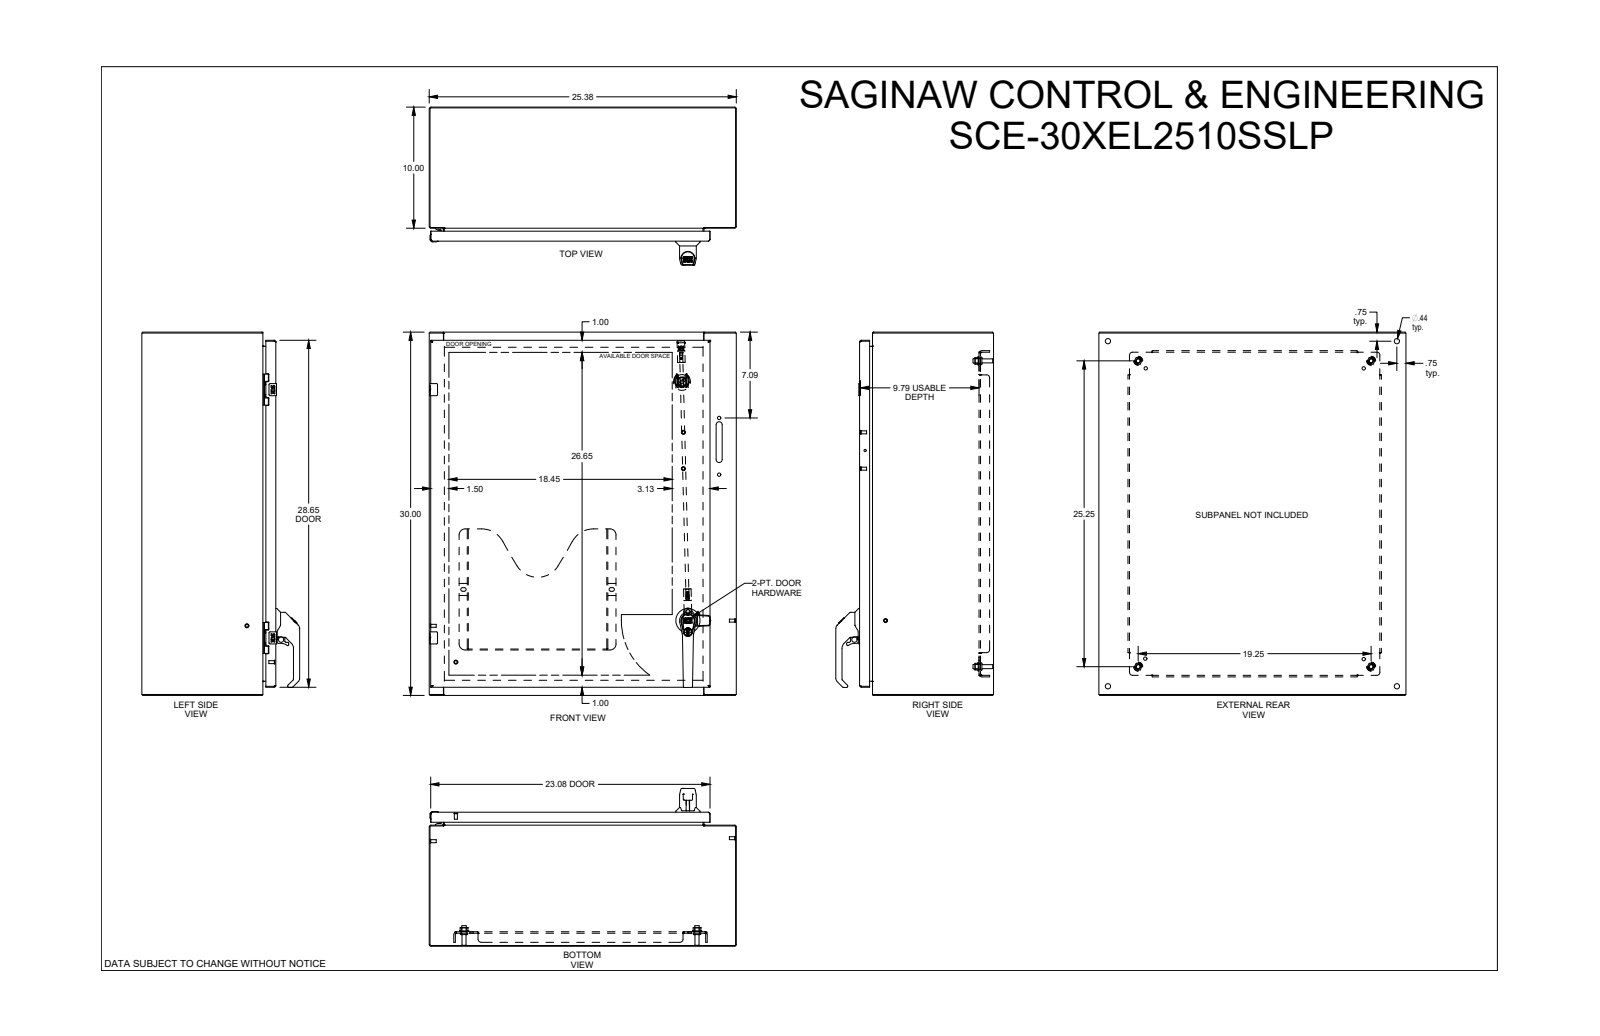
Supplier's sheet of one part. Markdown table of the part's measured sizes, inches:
| quantity | value |
| --- | --- |
| part name | SCE-30XEL2510SSLP |
| STEP written by | SolidWorks 2019 (CONFIG_CONTROL_DESIGN) |
| units | inches |
| bodies | 67 solids, 4628 faces (1743 planar, 1218 cylindrical, 1667 other) |
| overall size | 30 × 25.375 × 13.036 |
| volume | 329.1 in³ |
| surface area | 7 580 in² |
| round holes (diameter × count) | 0.281 × 6, 0.266 × 5, 0.172 × 4, 0.205 × 4, 0.244 × 4, 0.367 × 4, 0.437 × 4, 0.5 × 4, 0.25 × 3, 0.25 × 3, 0.375 × 3, 0.138 × 2 |
| round bosses / shafts (diameter × count) | 0.248 × 8, 0.17 × 6, 0.366 × 4, 0.332 × 4, 0.25 × 4, 0.563 × 3, 0.196 × 3, 0.341 × 2 |
| partial cylindrical surfaces (radius × count) | 0.03 × 69, 0.015 × 58, 0.01 × 36, 0.02 × 36, 0.02 × 34, 0.04 × 31, 0.039 × 30, 0.005 × 26 |
| main face-to-face distances | 0.075, 10.993, 10.918, 11.068, 1.125, 1.2, 9.868, 9.793, 0.075, 25.3 |
| hole center spacings | 20.5, 0.985, 0.02, 4.493, 0.472, 0.725, 0.854, 0.866 |
